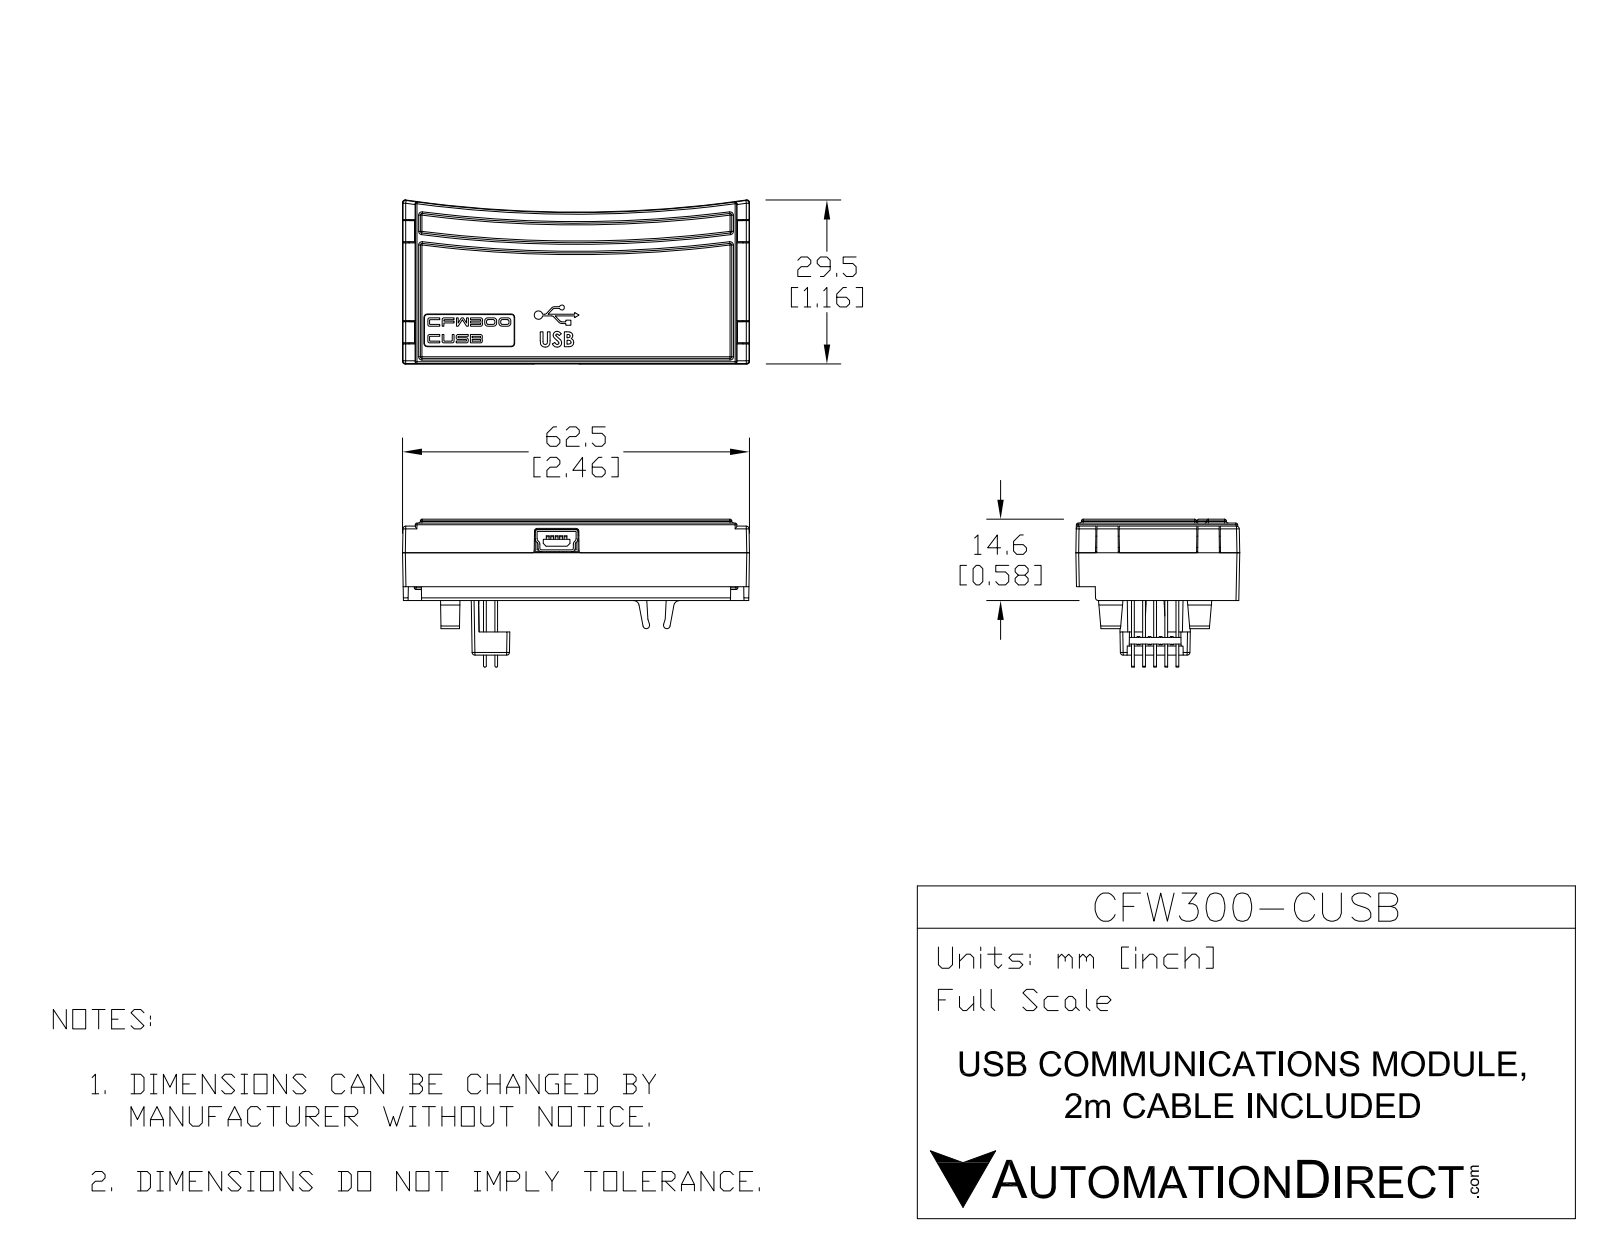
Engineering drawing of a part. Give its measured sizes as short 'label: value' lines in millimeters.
name: CFW300-CUSB
written by: SolidWorks 2017 (AUTOMOTIVE_DESIGN)
unit: mm
bodies: 1 solid, 444 faces (163 planar, 45 cylindrical, 236 other)
size: 62.5 × 29.4 × 14.6
volume: 24 020 mm³; area: 6 041 mm²
holes: 1× ⌀1.4, 1× ⌀2.2
bosses: 1× ⌀1.9, 1× ⌀1.2
rounds: 11× R1, 4× R0.5, 4× R0.5, 4× R0.6, 4× R0.6, 2× R0.8, 2× R0.9, 1× R217
face distances: 14.6, 2.3, 60.2, 2.5, 12.1, 57.9, 62.5, 3.4, 6.8, 4.3
hole spacings: 5.6
